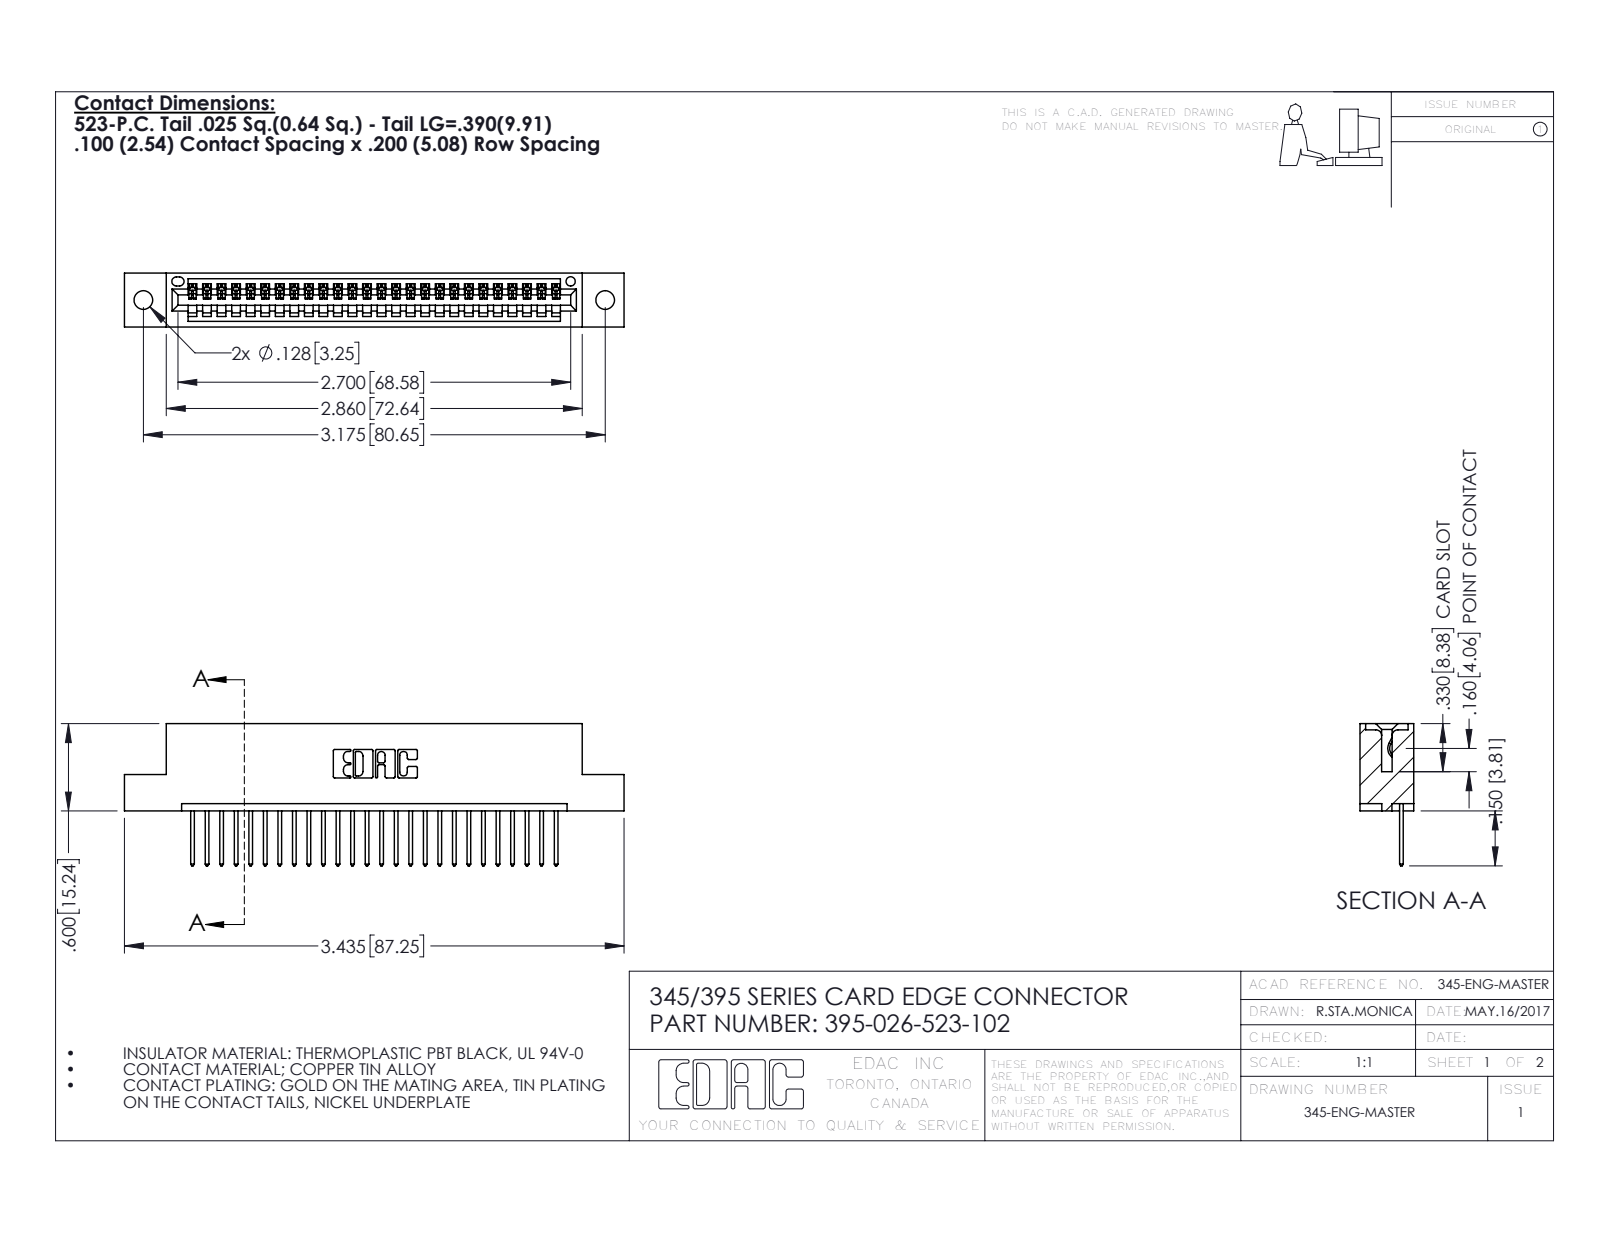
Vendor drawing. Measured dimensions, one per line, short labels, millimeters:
name: 345-292-001_345-293-123; 345 Part_Flush Mounting Lugs - 0.128 Dia; 395-026-523-102
written by: SolidWorks 2016 (CONFIG_CONTROL_DESIGN)
unit: mm
bodies: 27 solids, 1634 faces (1120 planar, 514 cylindrical, 0 other)
size: 87.2 × 24.8 × 9.4
volume: 8 110 mm³; area: 10 320 mm²
holes: 2× ⌀3.3, 1× ⌀1.6
rounds: 52× R0.2, 52× R0.3, 22× R0.3, 6× R0.2, 6× R0.8, 3× R0.7, 2× R0.8, 2× R1
face distances: 7.6, 1.8, 5.1, 9.4, 2.5, 6.9, 0.6, 5.7, 3.8, 1.8
hole spacings: 6.9, 74.7, 80.6
